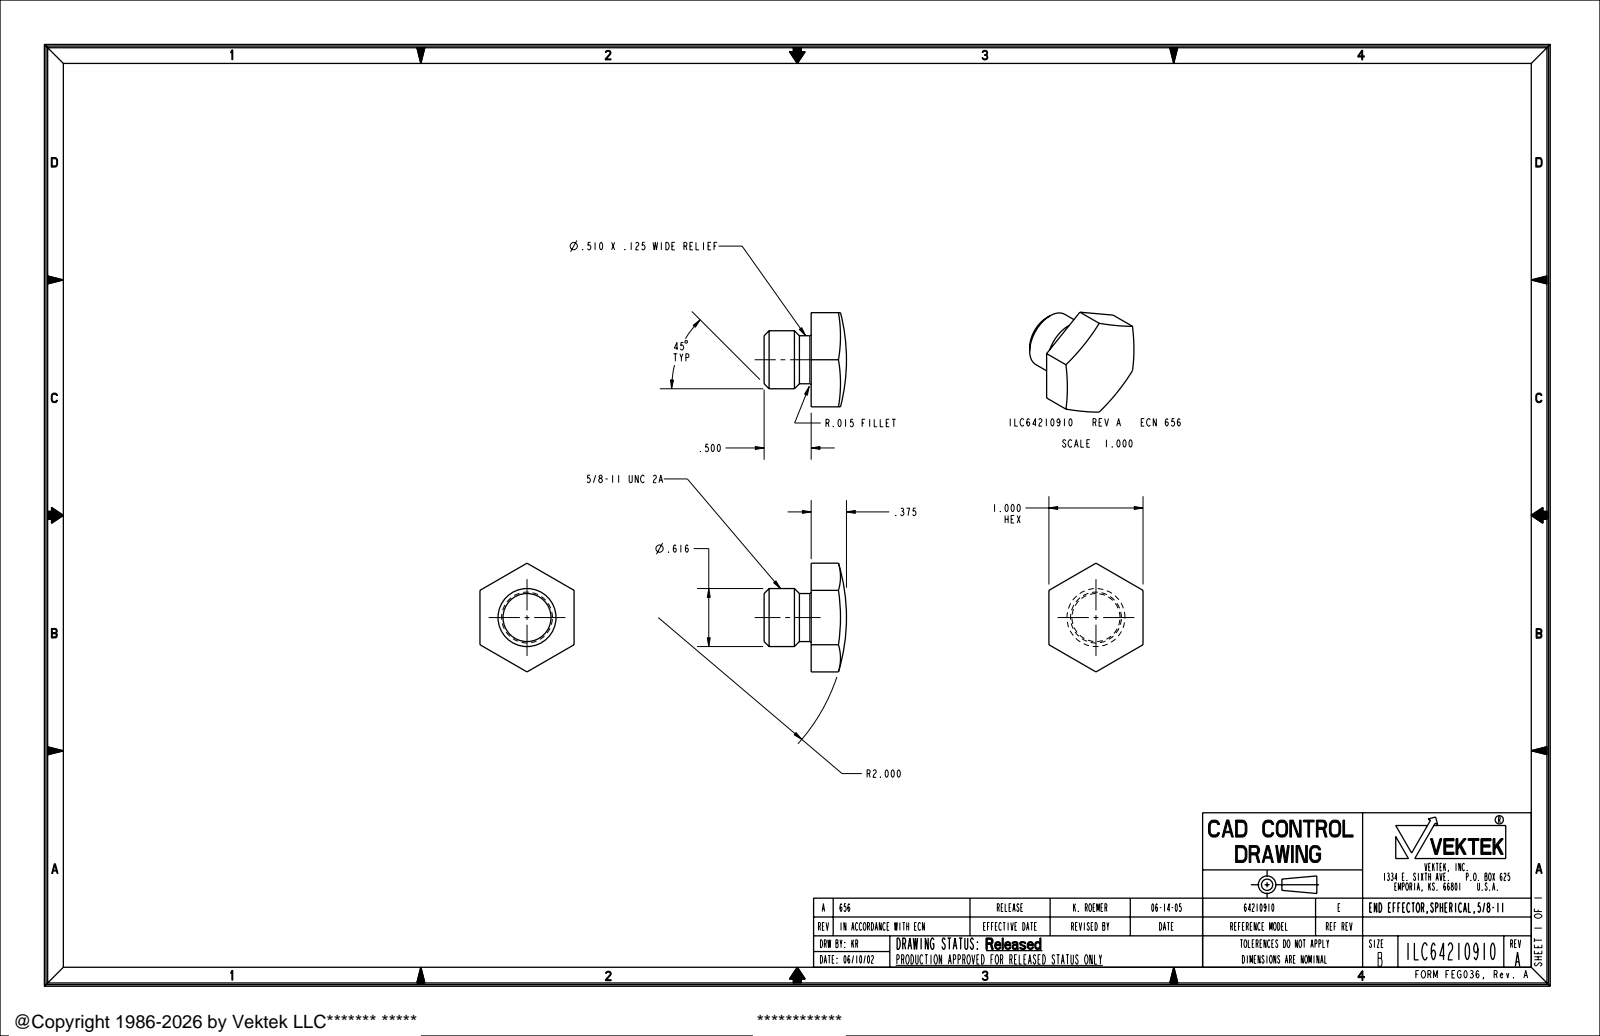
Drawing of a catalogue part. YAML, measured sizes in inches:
part_name: "ILC64210910"
step_written_by: "PRO/ENGINEER BY PARAMETRIC TECHNOLOGY CORPORATION, 2004290 (AUTOMOTIVE_DESIGN_CC2)"
units: inches
bodies: {solids: 1, faces: 20, planar: 8, cylindrical: 4, other: 8}
overall_size: [1.155, 1, 0.875]
volume: 0.427
surface_area: 3.778
round_bosses_or_shafts:
  - {diameter: 0.616, count: 1}
  - {diameter: 0.51, count: 1}
face_to_face_distances: [1, 0.5]
